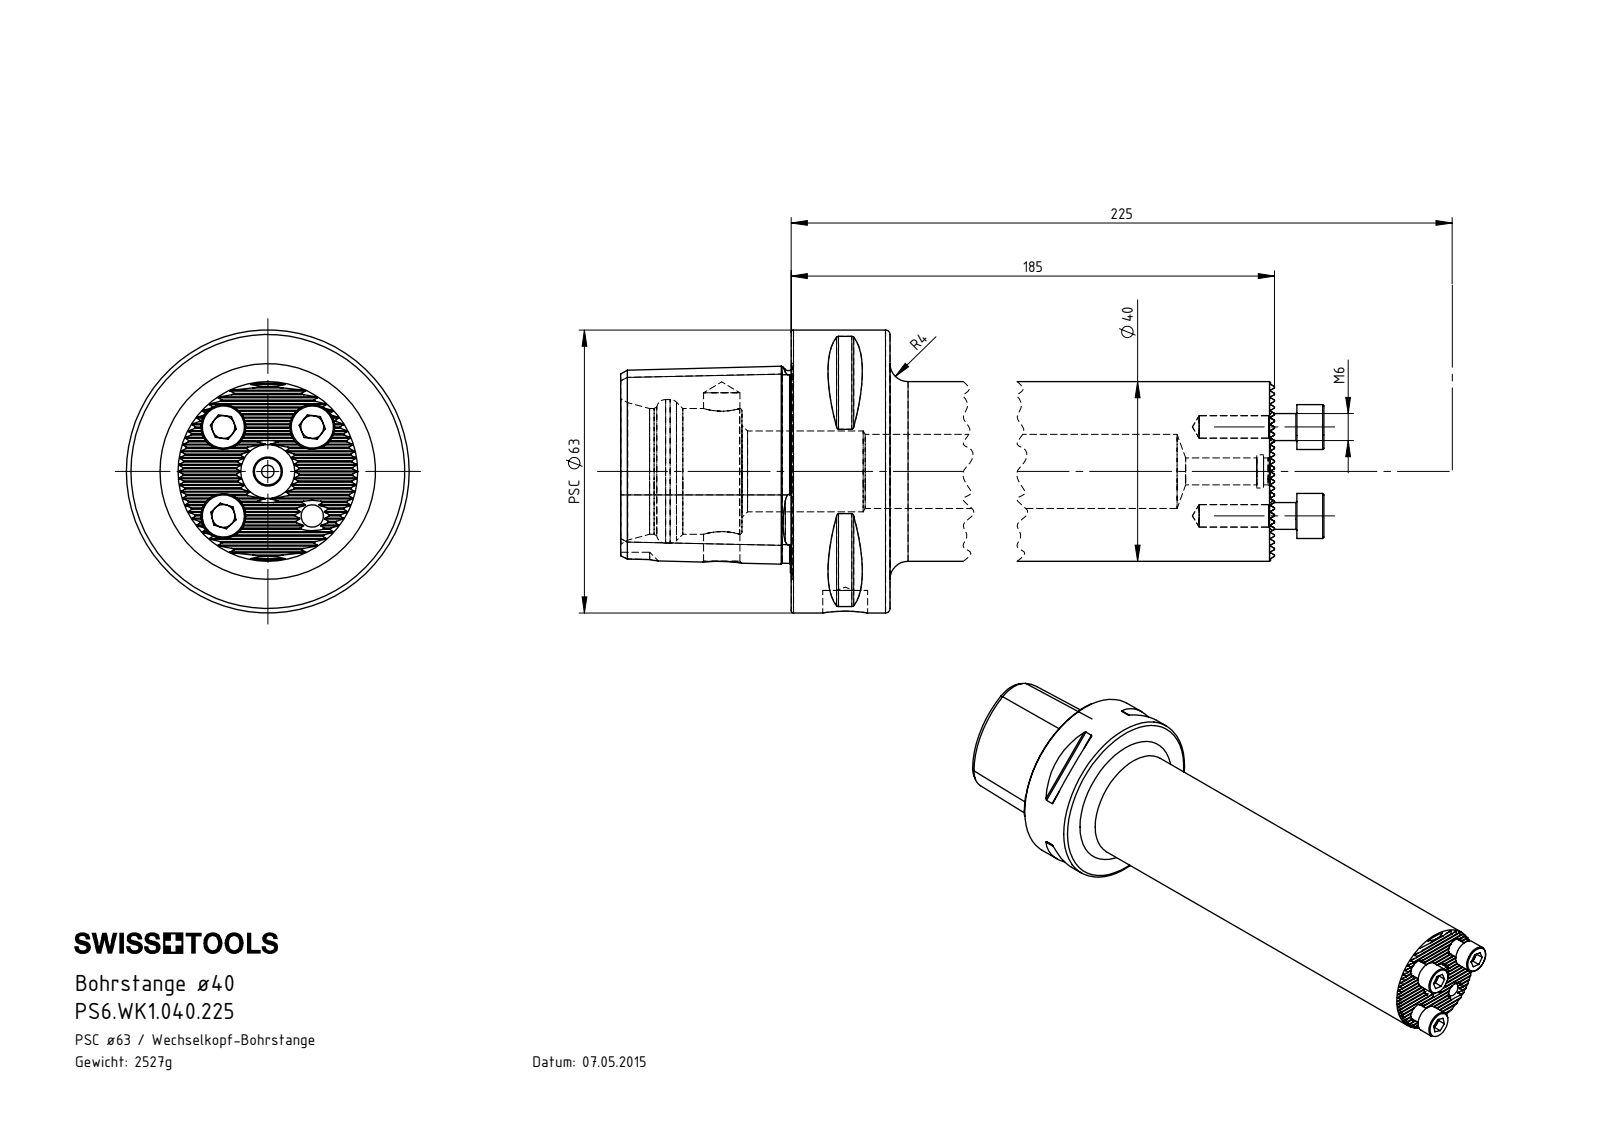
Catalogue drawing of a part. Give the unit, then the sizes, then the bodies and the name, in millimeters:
Units: millimetres
Overall size (bounding box): 234.4 × 63 × 63
Round holes (diameter × count): ⌀5 ×4, ⌀3 ×1, ⌀4 ×1, ⌀6 ×1, ⌀7.4 ×1, ⌀8.1 ×1, ⌀16.5 ×1, ⌀18 ×1, ⌀28 ×1, ⌀32 ×1
Round bosses / shafts (diameter × count): ⌀10 ×3, ⌀6 ×3, ⌀63 ×1, ⌀40 ×1, ⌀16 ×1
Partial cylindrical surfaces — rounded edges, fillets, slot ends (radius × count): R0.12 ×27, R0.5 ×8, R6 ×1
Main face-to-face distances: 22, 1.3, 2.6, 3.9, 5.2, 12.99, 11, 38, 60, 9.09
Hole centre spacings: 14, 19.8, 28, 27.5
Volume: 298 447 mm³ · Surface area: 61 426 mm²
Bodies: 7 solids, 473 faces (231 planar, 113 cylindrical, 129 other)
Part name (STEP PRODUCT): PS6.WK1.040.225; WK1-ER1.016.002_A_Fertigbearbeitung; ISO 4762 - M6 x 16; DIN 3771 - 6x1 (+2 more)
STEP written by: SolidWorks 2017 (AUTOMOTIVE_DESIGN)
